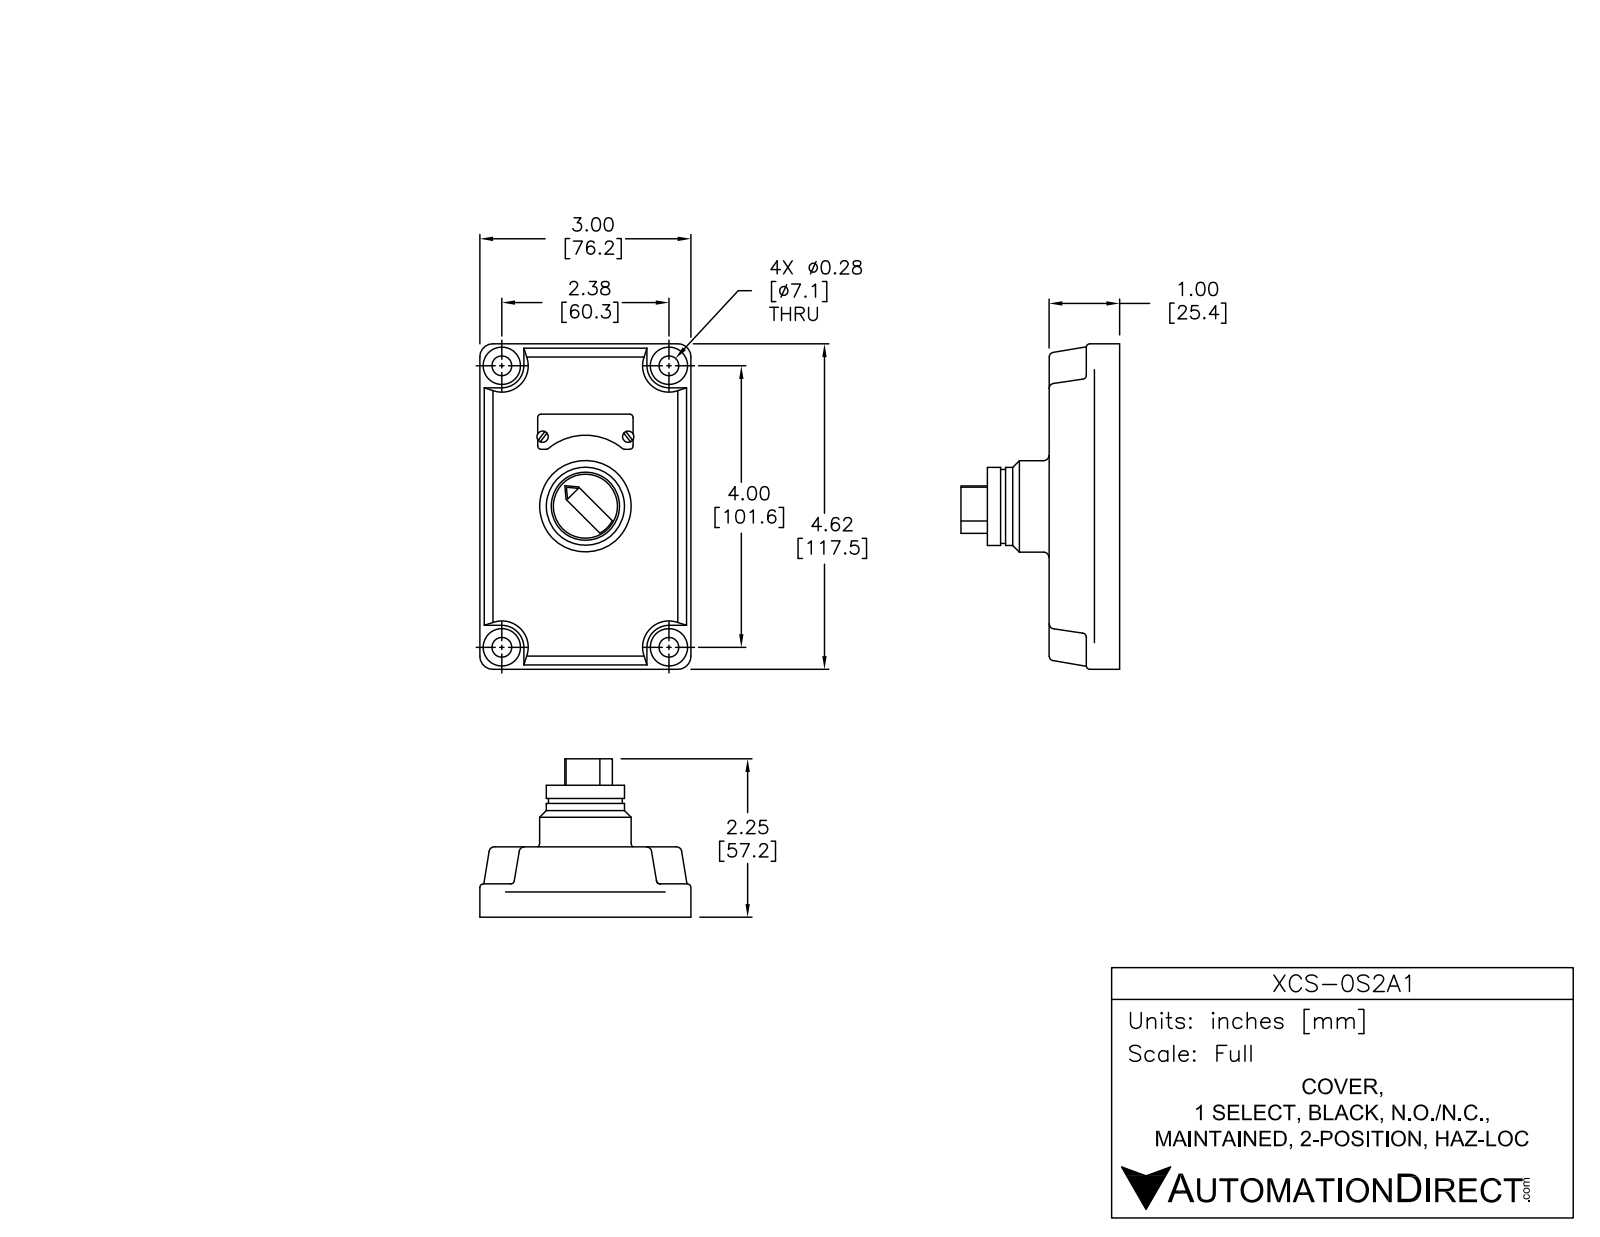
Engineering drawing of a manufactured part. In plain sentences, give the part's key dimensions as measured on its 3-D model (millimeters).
The part is named "XCS-0S2A1". Its 3-D file was written by "SolidWorks 2015 (AUTOMOTIVE_DESIGN)". It is 10 solids with 500 faces: 203 planar, 166 cylindrical and 131 other. Overall it measures 117.6 by 95.04 by 78.74 millimeters. Its volume is 212 200 cubic millimeters and its surface area 55 562 square millimeters. Round holes: 4 of diameter 6.86, 1 of diameter 14.5, 1 of diameter 24.64. Round bosses or shafts: 8 of diameter 3.3, 4 of diameter 11.6, 4 of diameter 6.35, 1 of diameter 33.02, 1 of diameter 28.19, 1 of diameter 26.67, 1 of diameter 24, 1 of diameter 23.11. Partial cylindrical surfaces (rounded edges, fillets, slot ends): 28 of radius 0.25, 10 of radius 1.27, 8 of radius 0.51, 8 of radius 1.4, 4 of radius 2.54, 4 of radius 3.5, 4 of radius 9.65, 4 of radius 15.24. The main face-to-face distances are 13.34, 12.7, 26.04, 0.63, 7.5, 26.67, 13.97, 5.2, 20.84, 21.47. The hole center spacings are 59.11, 60.46, 101.6, 118.23.
